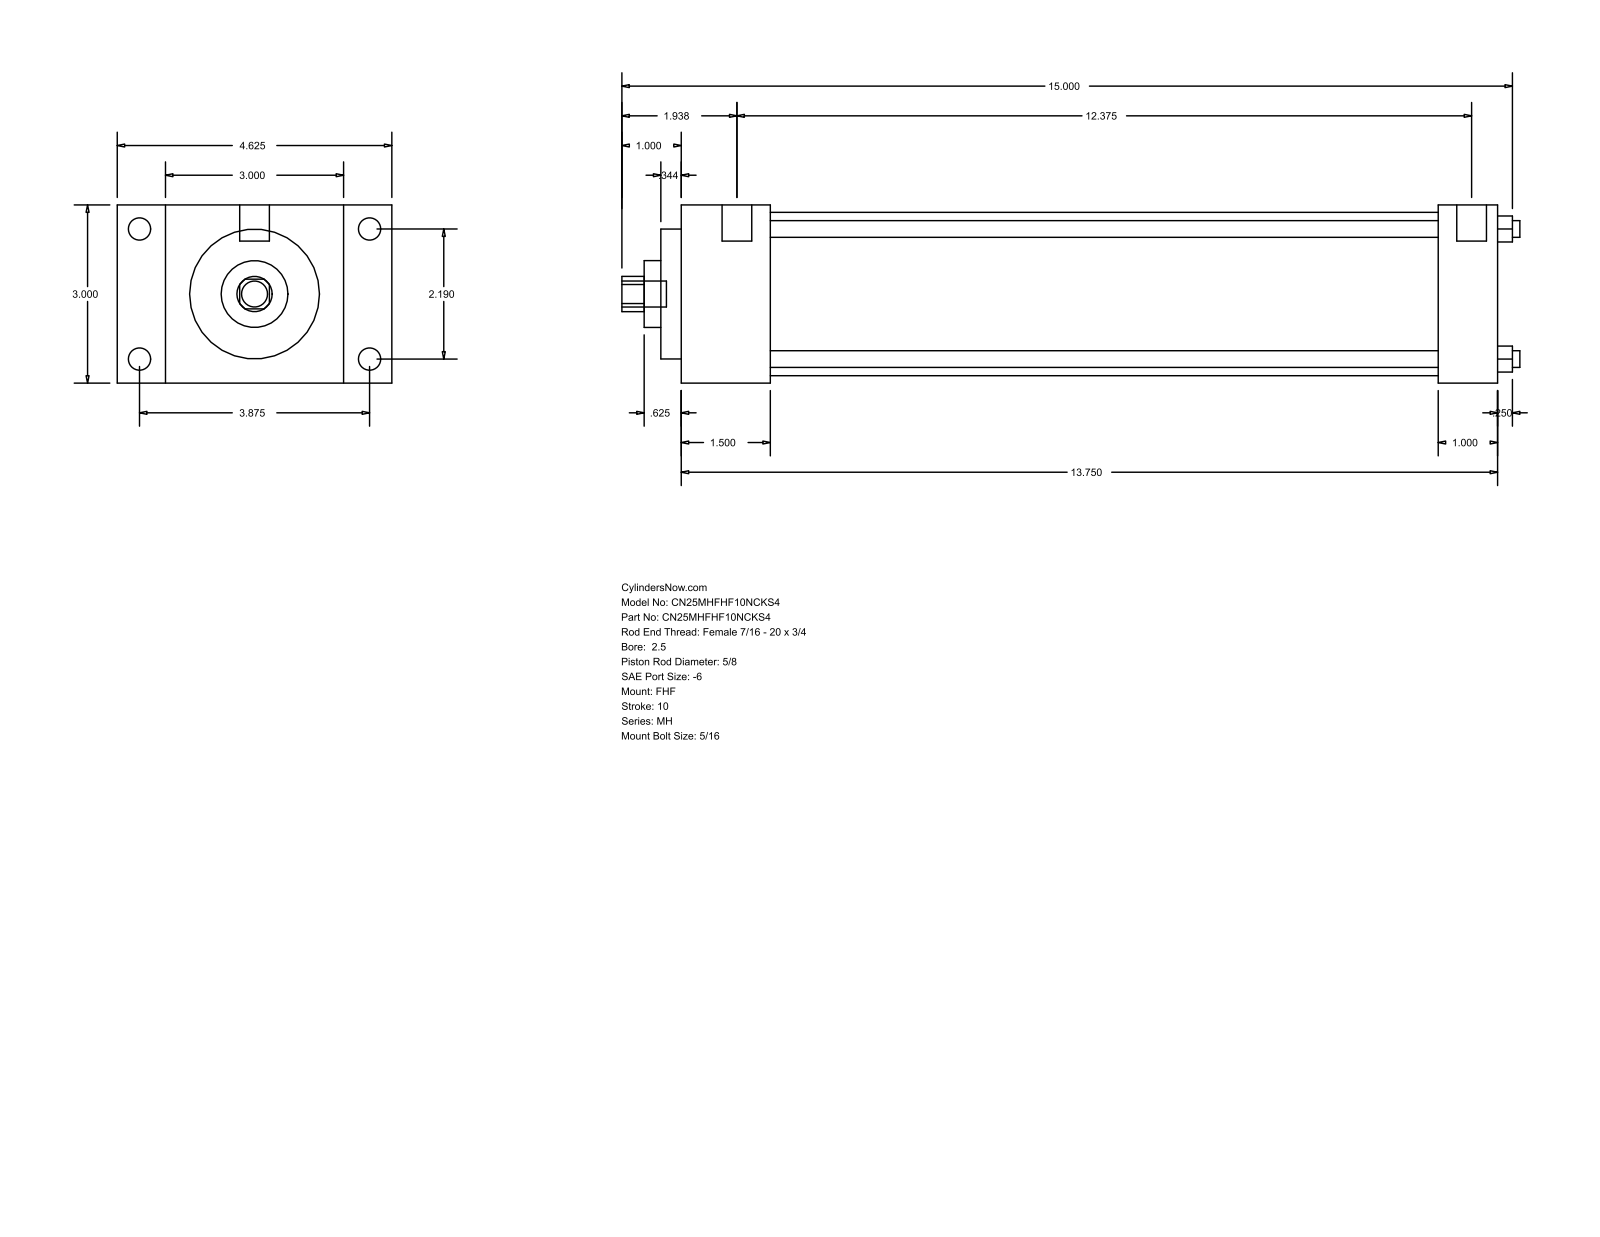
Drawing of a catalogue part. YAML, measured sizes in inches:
part_name: "MH_FHF__0250_0.625"
step_written_by: "GSSL Pune (CONFIG_CONTROL_DESIGN)"
units: inches
bodies: {solids: 0, faces: 90, planar: 61, cylindrical: 29, other: 0}
overall_size: [15.125, 4.625, 3]
round_holes:
  - {diameter: 0.281, count: 4}
  - {diameter: 0.625, count: 1}
  - {diameter: 1.125, count: 1}
  - {diameter: 2.187, count: 1}
  - {diameter: 2.75, count: 1}
round_bosses_or_shafts:
  - {diameter: 0.375, count: 4}
  - {diameter: 0.219, count: 4}
  - {diameter: 0.5, count: 2}
  - {diameter: 0.437, count: 1}
partial_cylinders:
  - {radius: 0.297, count: 1}
face_to_face_distances: [3, 13.75, 1.5, 12.25, 0.813, 3.813, 4.625, 1, 12.75, 11.25]
hole_center_spacings: [1.548, 2.19, 3.097]
